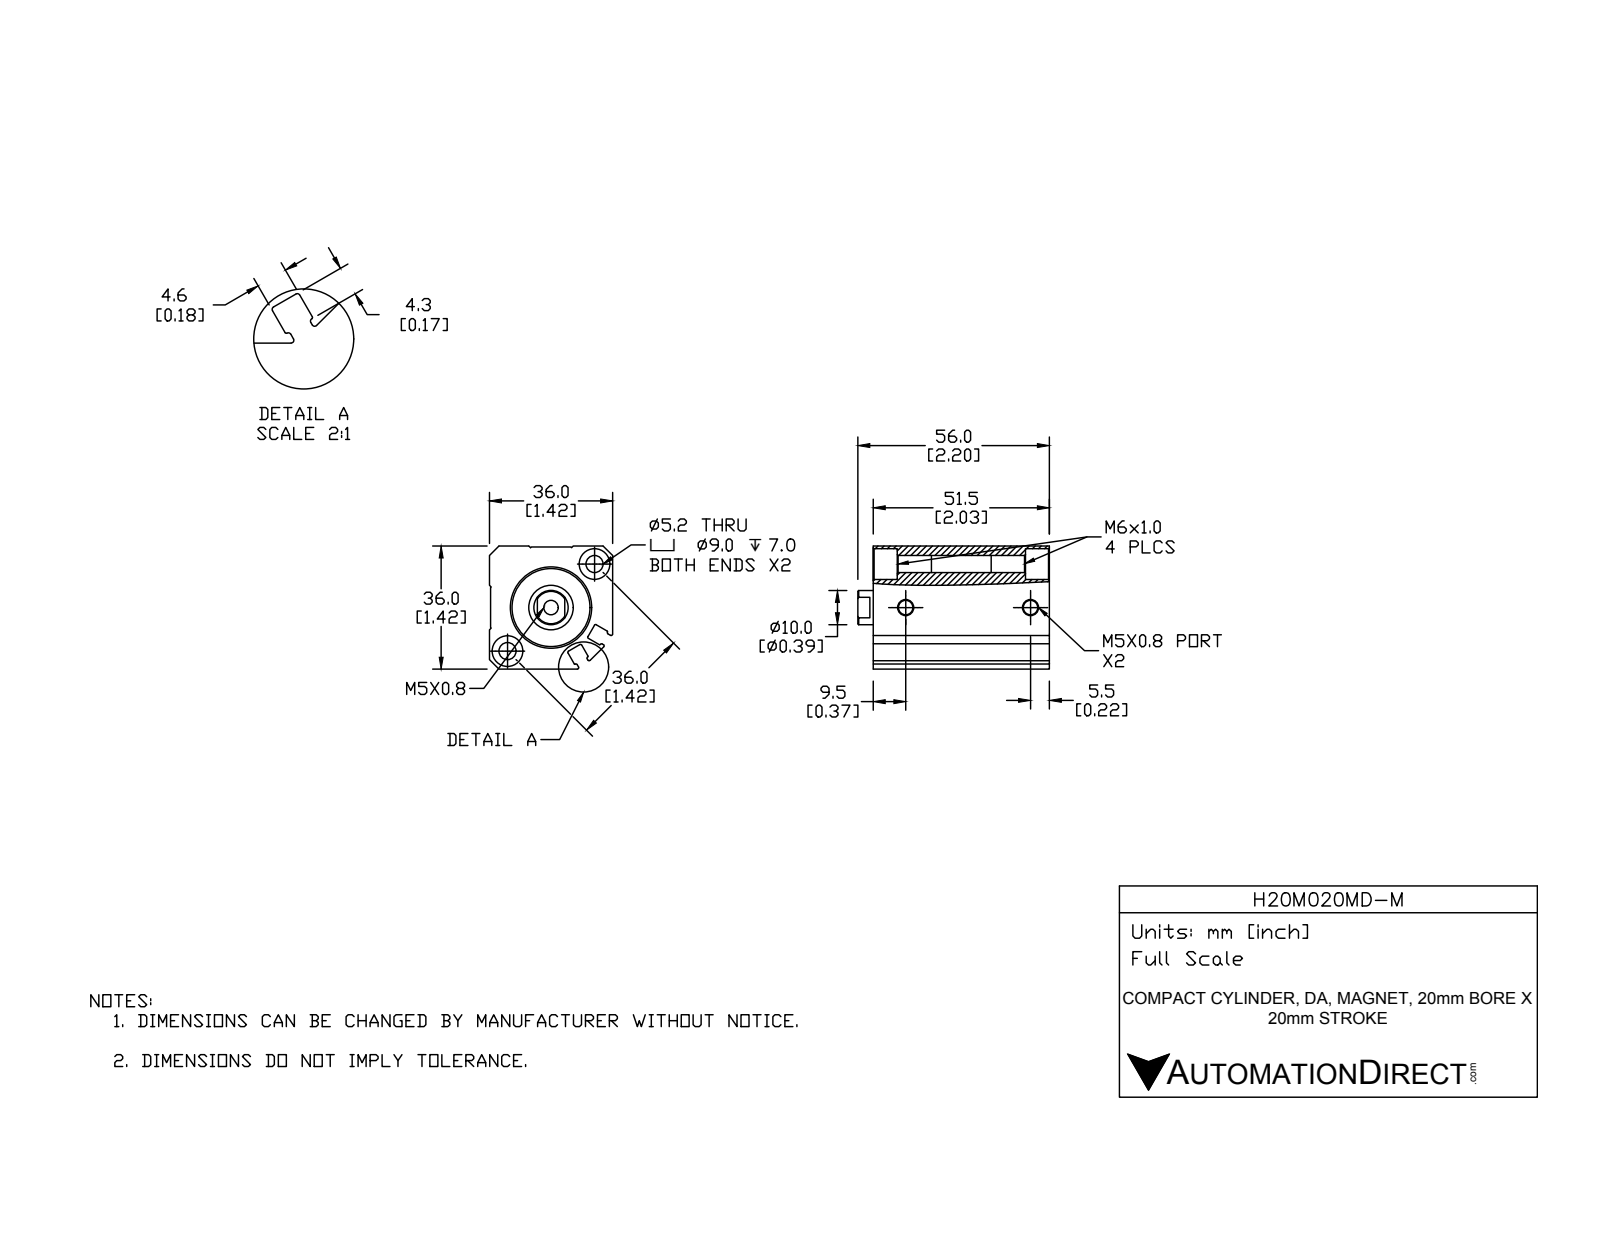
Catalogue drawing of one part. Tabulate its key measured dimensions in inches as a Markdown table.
| quantity | value |
| --- | --- |
| part name | H20M020MD-M-BODY; H20M020MD-M-PISTON; H20M020MD-M |
| STEP written by | SolidWorks 2015 (CONFIG_CONTROL_DESIGN) |
| units | inches |
| bodies | 2 solids, 141 faces (53 planar, 55 cylindrical, 33 other) |
| overall size | 2.205 × 1.417 × 1.417 |
| volume | 3.158 in³ |
| surface area | 29.49 in² |
| round holes (diameter × count) | 0.165 × 3, 0.197 × 2, 0.354 × 2, 0.394 × 1, 0.512 × 1, 0.787 × 1, 0.898 × 1 |
| round bosses / shafts (diameter × count) | 0.433 × 1 |
| partial cylindrical surfaces (radius × count) | 0.016 × 12, 0.008 × 4 |
| main face-to-face distances | 1.417, 1.406, 0.157, 2.028, 1.87, 0.102, 0.181, 0.055, 1.972, 1.594 |
| hole center spacings | 0.709, 1.418, 1.437 |
